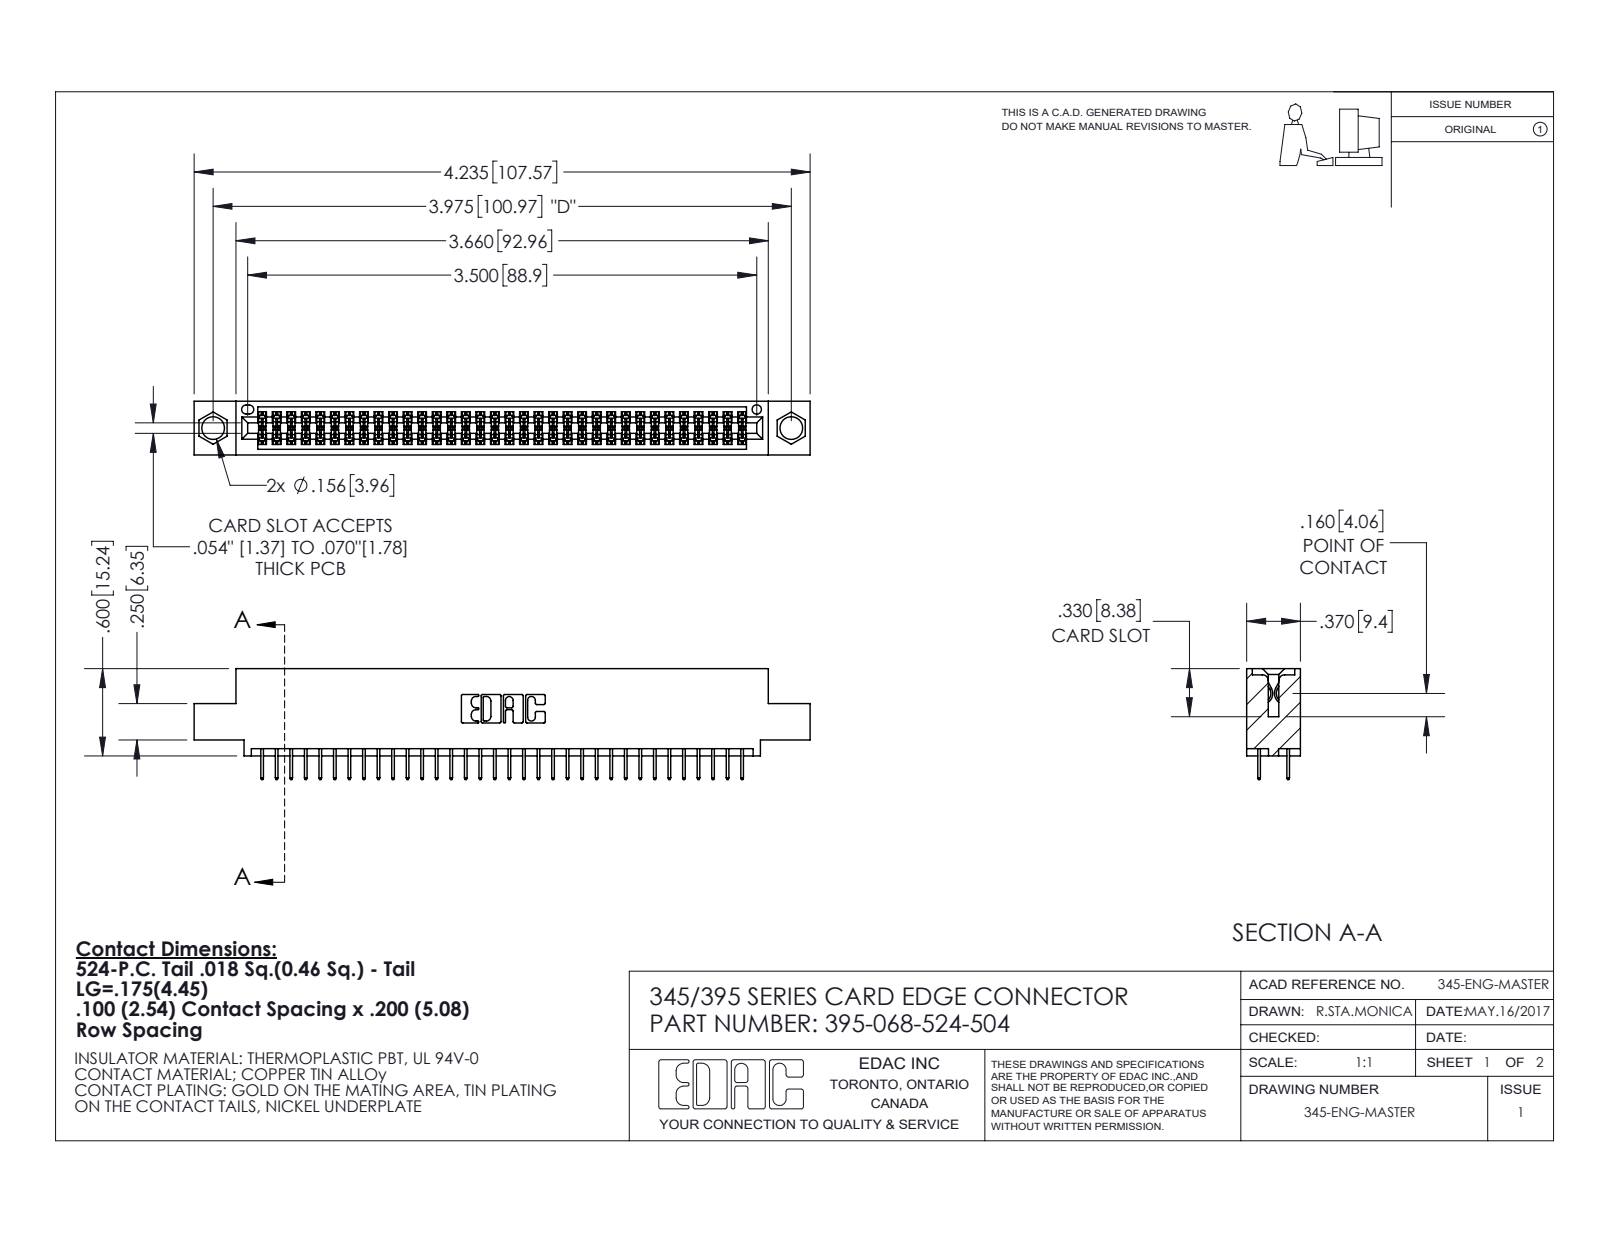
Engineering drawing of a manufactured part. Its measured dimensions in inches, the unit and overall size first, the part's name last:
Units: inches
Overall size (bounding box): 4.235 × 0.762 × 0.37
Round holes (diameter × count): ⌀0.156 ×2, ⌀0.064 ×1
Partial cylindrical surfaces — rounded edges, fillets, slot ends (radius × count): R0.006 ×102, R0.01 ×22, R0.007 ×6, R0.031 ×6, R0.026 ×3, R0.014 ×2, R0.019 ×2, R0.022 ×2
Main face-to-face distances: 0.072, 0.298, 0.2, 0.37, 0.098, 0.272, 0.025, 0.225, 0.072, 0.175
Hole centre spacings: 0.27, 3.74, 3.975
Volume: 0.616 in³ · Surface area: 22.38 in²
Bodies: 69 solids, 3816 faces (2750 planar, 1066 cylindrical, 0 other)
Part name (STEP PRODUCT): 345 Part_0.110 Offset - 0.156 Dia-TI; 395-068-524-504; 345-292-001_345-293-124
STEP written by: SolidWorks 2020 (CONFIG_CONTROL_DESIGN)
